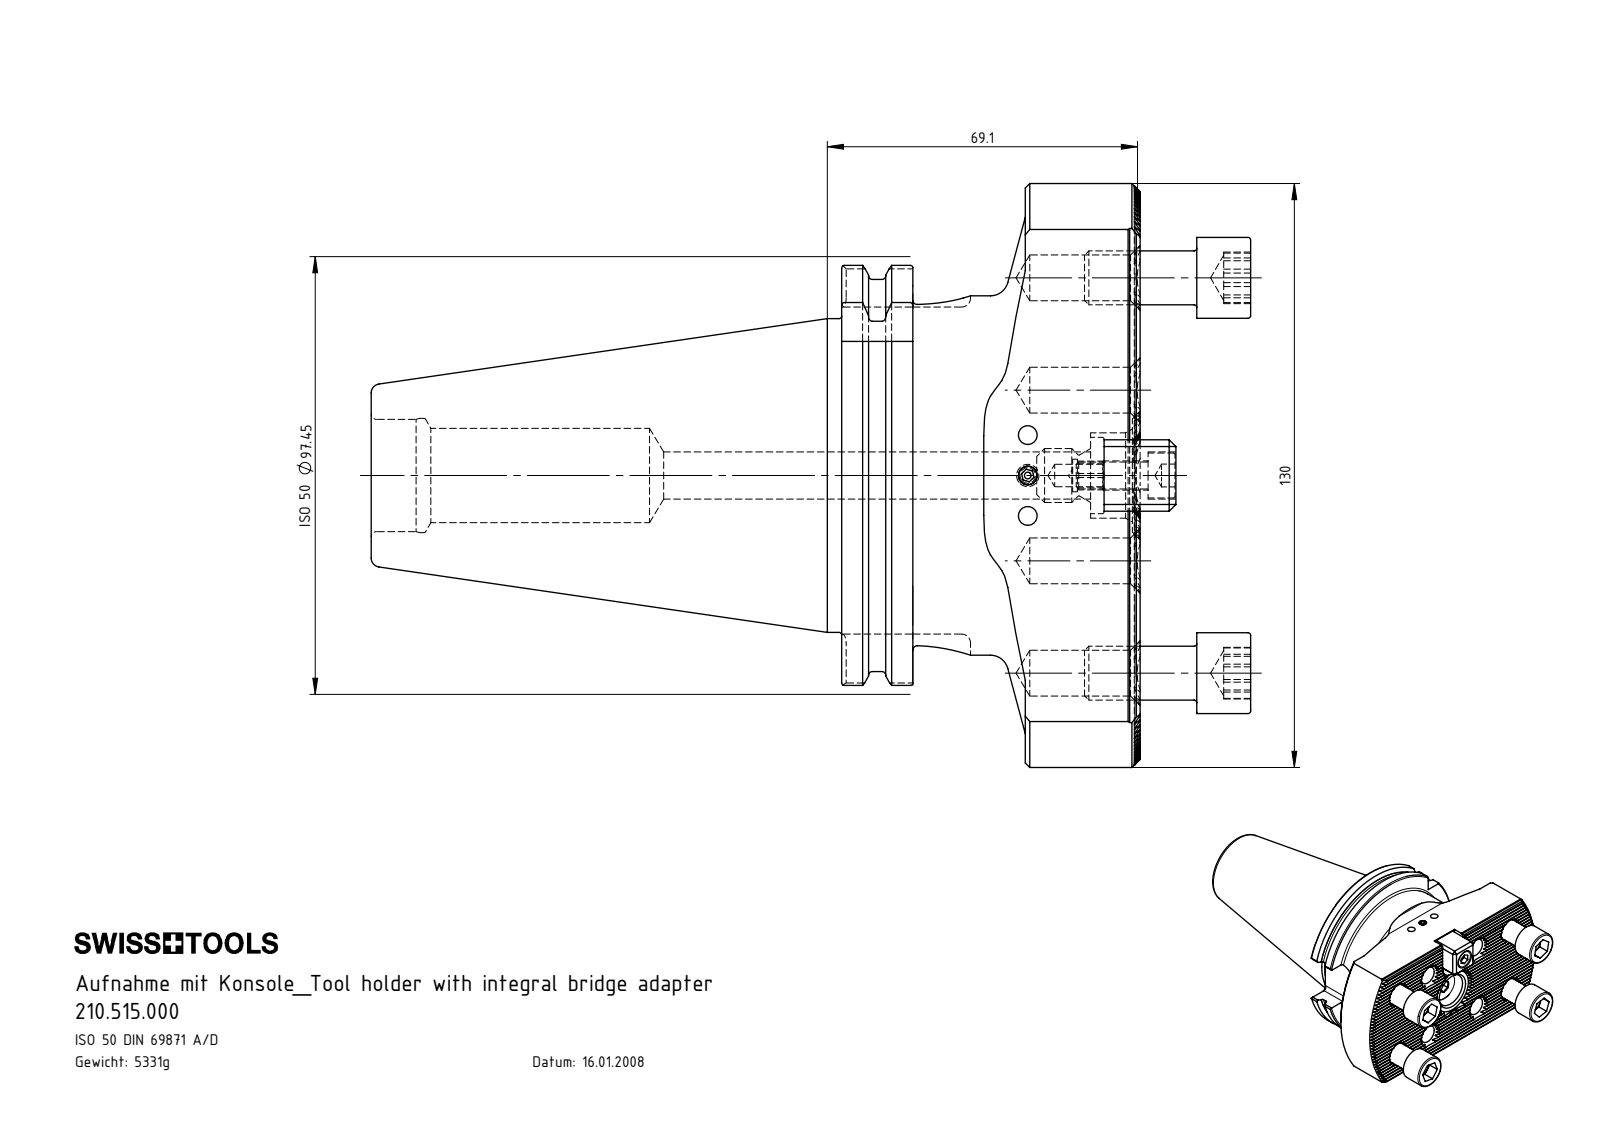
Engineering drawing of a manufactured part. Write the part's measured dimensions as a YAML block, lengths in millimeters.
part_name: "DIN 908 - M12x1.5; ISO 4762 - M12 x 25; ISO 4762 - M6 x 16; Ko1-ER1.001.016_A (+3 more)"
step_written_by: "SolidWorks 2017 (CONFIG_CONTROL_DESIGN)"
units: millimeters
bodies: {solids: 10, faces: 888, planar: 503, cylindrical: 213, other: 172}
overall_size: [195.9, 130, 97.45]
volume: 679040
surface_area: 91499
round_holes:
  - {diameter: 10.2, count: 8}
  - {diameter: 4.2, count: 3}
  - {diameter: 10.5, count: 2}
  - {diameter: 1.5, count: 1}
  - {diameter: 5, count: 1}
  - {diameter: 6.5, count: 1}
  - {diameter: 7.24, count: 1}
  - {diameter: 19, count: 1}
  - {diameter: 21, count: 1}
  - {diameter: 25, count: 1}
  - {diameter: 25.45, count: 1}
round_bosses_or_shafts:
  - {diameter: 12, count: 5}
  - {diameter: 18, count: 4}
  - {diameter: 91, count: 1}
  - {diameter: 80, count: 1}
  - {diameter: 69.85, count: 1}
  - {diameter: 17, count: 1}
  - {diameter: 10, count: 1}
  - {diameter: 6, count: 1}
partial_cylinders:
  - {radius: 0.14, count: 34}
  - {radius: 2, count: 8}
  - {radius: 4, count: 2}
  - {radius: 7.95, count: 1}
  - {radius: 12.85, count: 1}
  - {radius: 48.73, count: 1}
  - {radius: 65, count: 1}
face_to_face_distances: [1.73, 17.32, 70, 8.66, 3.46, 5.2, 6.93, 15.59, 19.05, 3.47]
hole_center_spacings: [25, 27.59, 40, 47.17, 48.33, 63, 74.63, 9]
